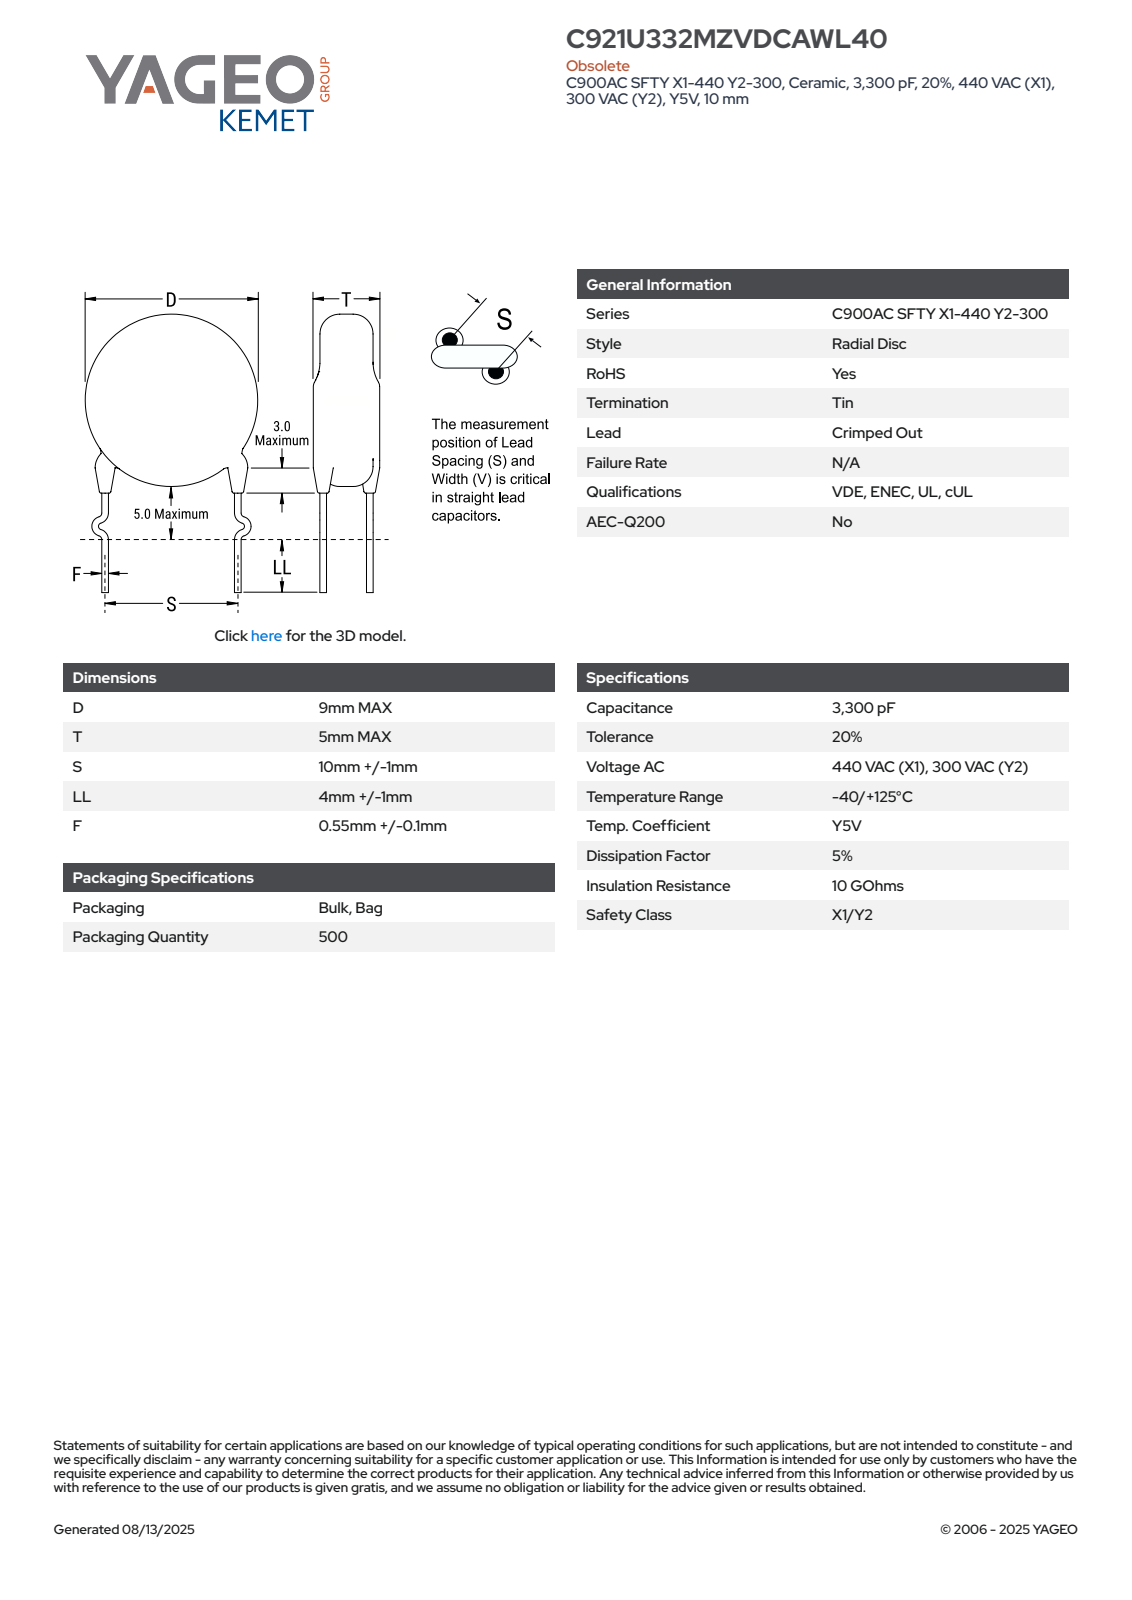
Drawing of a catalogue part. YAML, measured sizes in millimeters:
part_name: "CCD_KCOC900_D9T5S10LL5F0.55"
step_written_by: "SolidWorks 2014 (AUTOMOTIVE_DESIGN)"
units: millimeters
bodies: {solids: 4, faces: 93, planar: 63, cylindrical: 10, other: 20}
overall_size: [19, 14.51, 5.85]
volume: 322
surface_area: 324
round_bosses_or_shafts:
  - {diameter: 1.2, count: 2}
  - {diameter: 9, count: 1}
partial_cylinders:
  - {radius: 0.6, count: 2}
face_to_face_distances: [5, 0.94, 4.98, 4.04, 0.76, 3.82, 0.58, 4.07, 2.77, 2.88]
